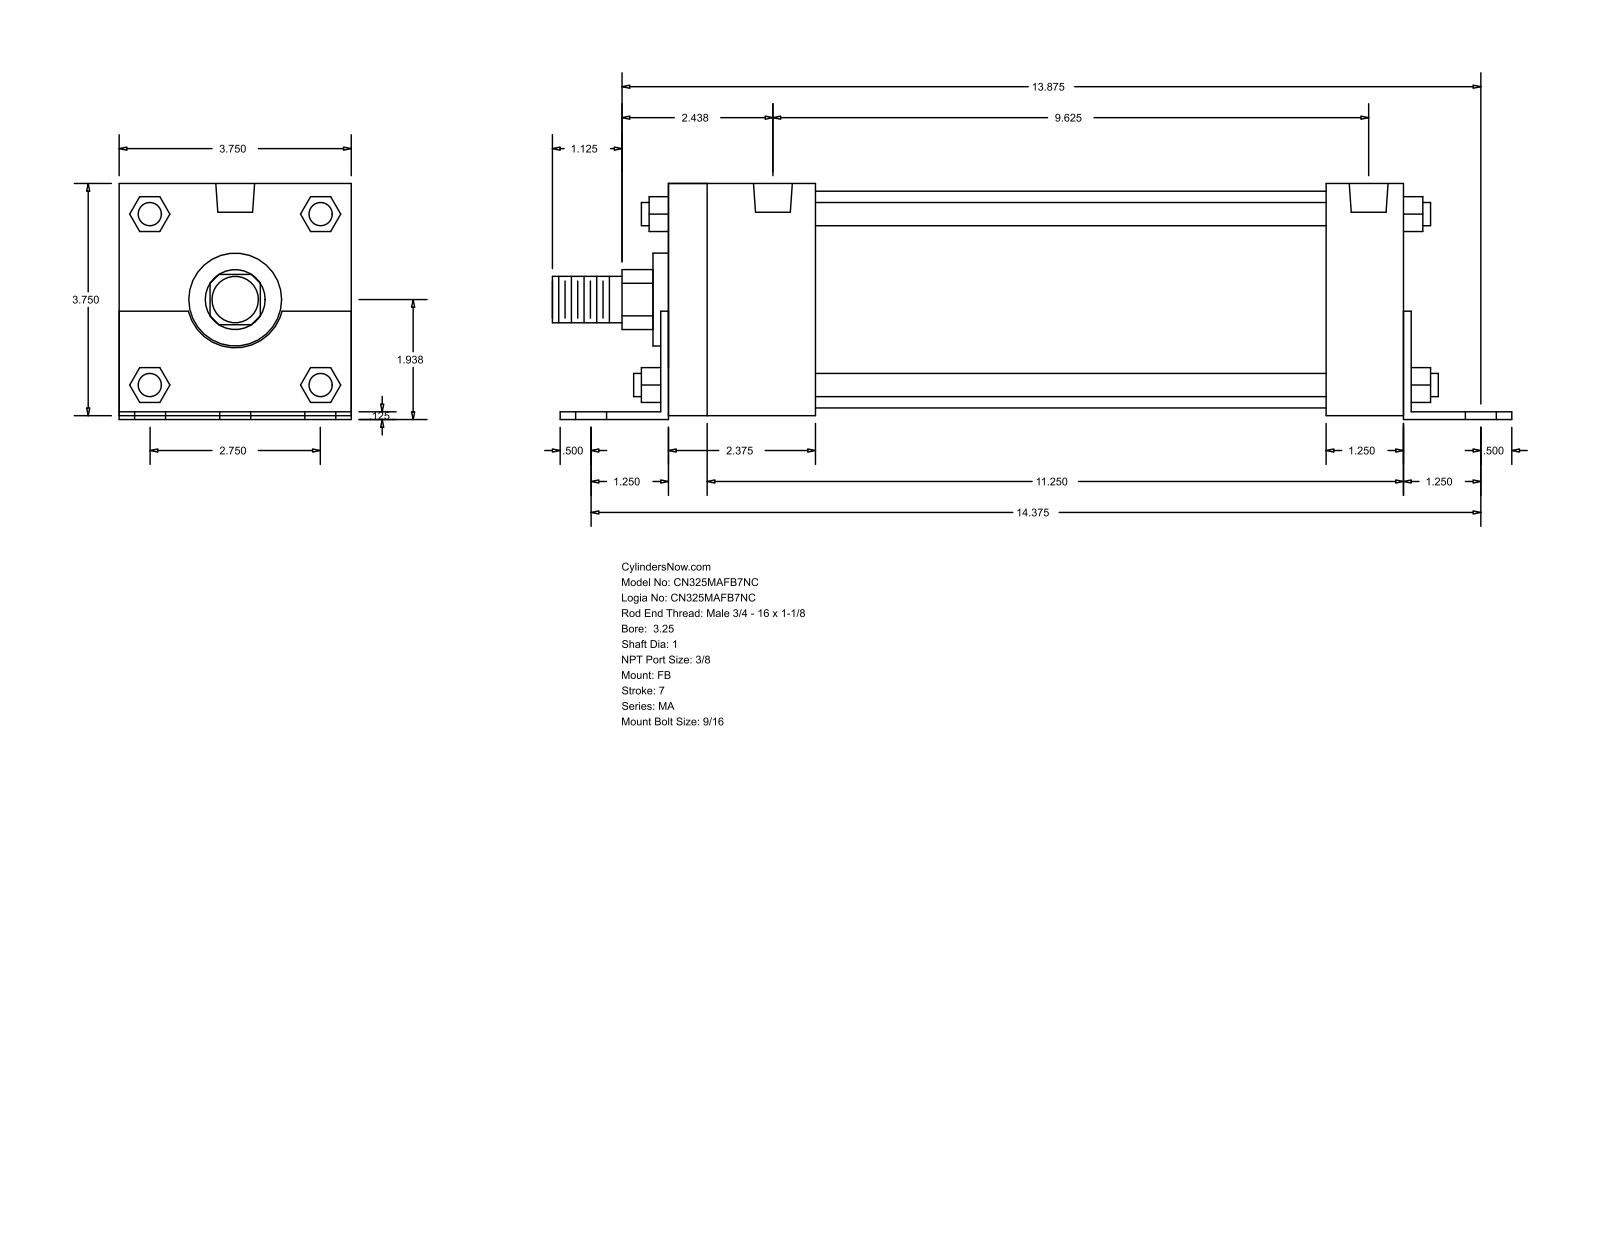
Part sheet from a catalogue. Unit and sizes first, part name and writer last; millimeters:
Units: millimetres
Overall size (bounding box): 393.7 × 96.84 × 95.25
Round holes (diameter × count): ⌀14.29 ×6, ⌀11.11 ×4, ⌀15.93 ×2
Round bosses / shafts (diameter × count): ⌀9.53 ×4, ⌀88.9 ×1, ⌀38.1 ×1, ⌀25.4 ×1, ⌀19.05 ×1
Partial cylindrical surfaces — rounded edges, fillets, slot ends (radius × count): R12.29 ×1, R19.81 ×1
Main face-to-face distances: 95.24, 3.17, 1.59, 96.83, 1.58, 93.66, 304.8, 301.63, 307.97, 273.05
Hole centre spacings: 34.92, 366.8, 365.13, 57.78, 61.65, 69.84, 82.38, 86.71
Bodies: 0 solids, 140 faces (105 planar, 35 cylindrical, 0 other)
Part name (STEP PRODUCT): MA_FB__0325_1
STEP written by: GSSL Pune (CONFIG_CONTROL_DESIGN)
